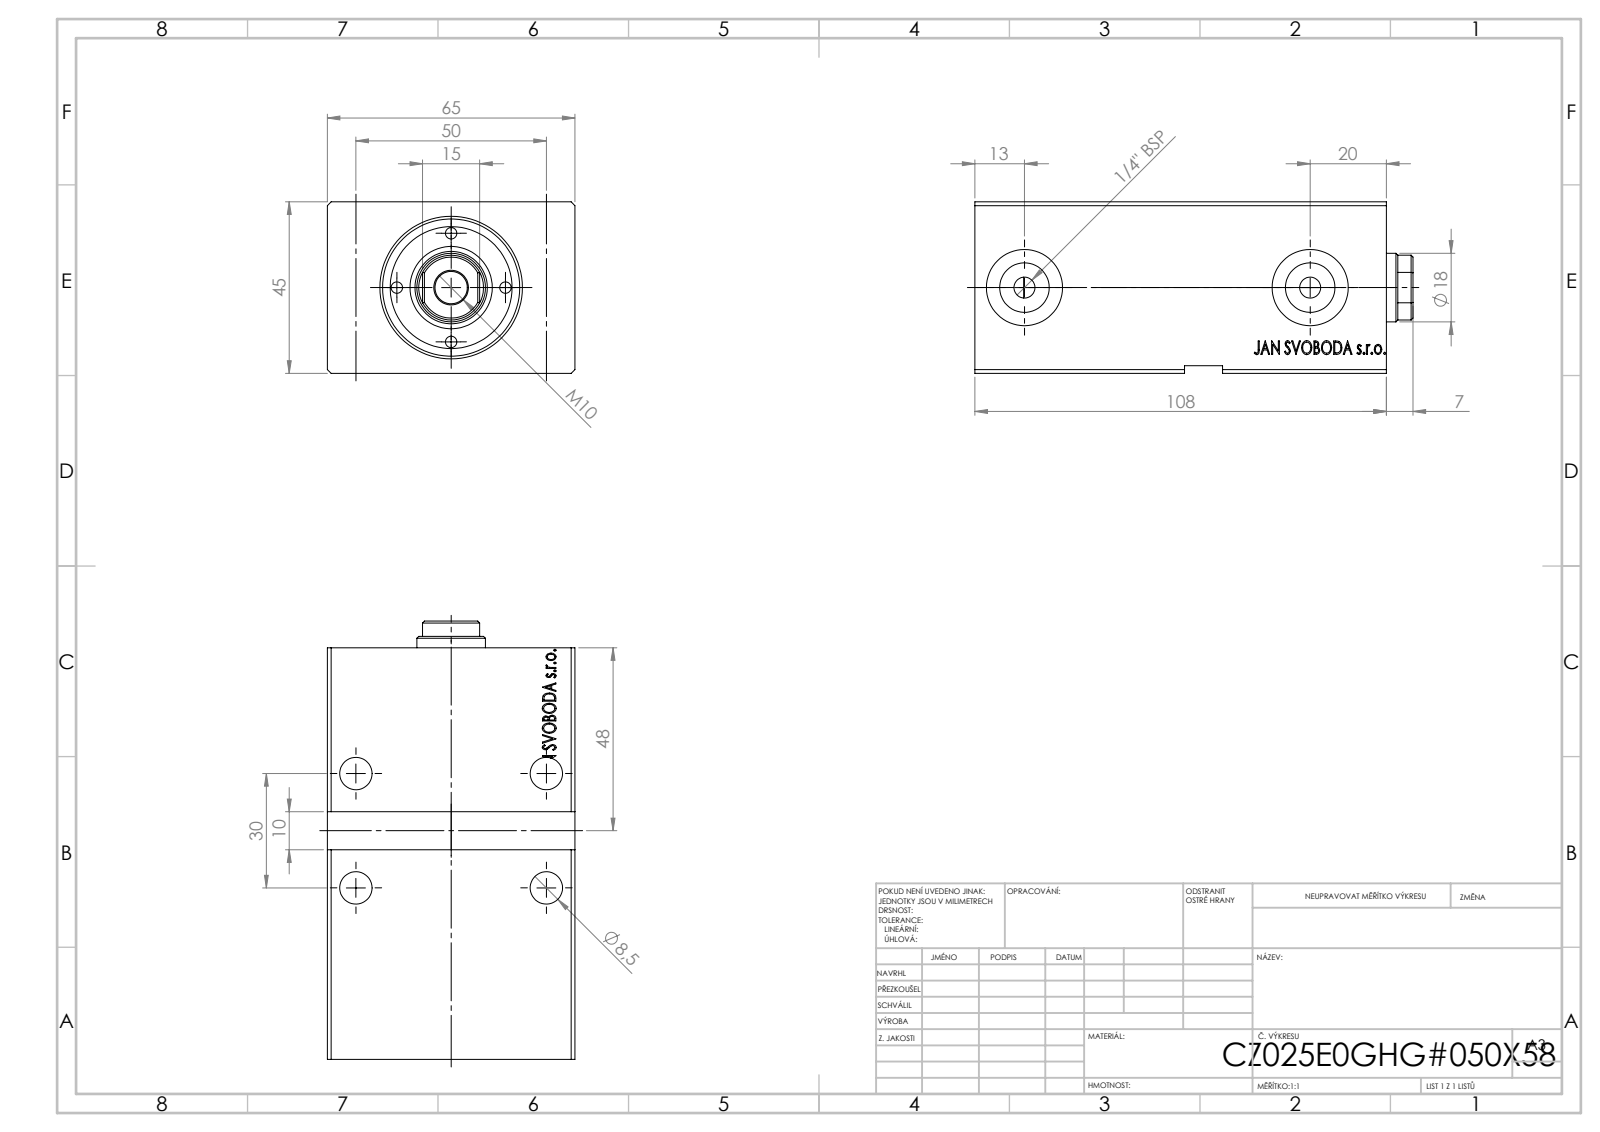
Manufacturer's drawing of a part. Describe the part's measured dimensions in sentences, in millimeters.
Its 3-D file was written by "SolidWorks 2019 (CONFIG_CONTROL_DESIGN)". It is 1 solid with 770 faces: 372 planar, 26 cylindrical and 372 other. Overall it measures 108 by 65 by 45 millimeters. Its volume is 222 141 cubic millimeters and its surface area 44 804 square millimeters. Round holes: 4 of diameter 8.5, 2 of diameter 5.5, 2 of diameter 13, 2 of diameter 20, 1 of diameter 25, 1 of diameter 36. The main face-to-face distances are 45, 65, 108, 107.8, 2, 43, 58, 49.8, 50, 96.5. The hole center spacings are 30, 50, 58.31, 75.
